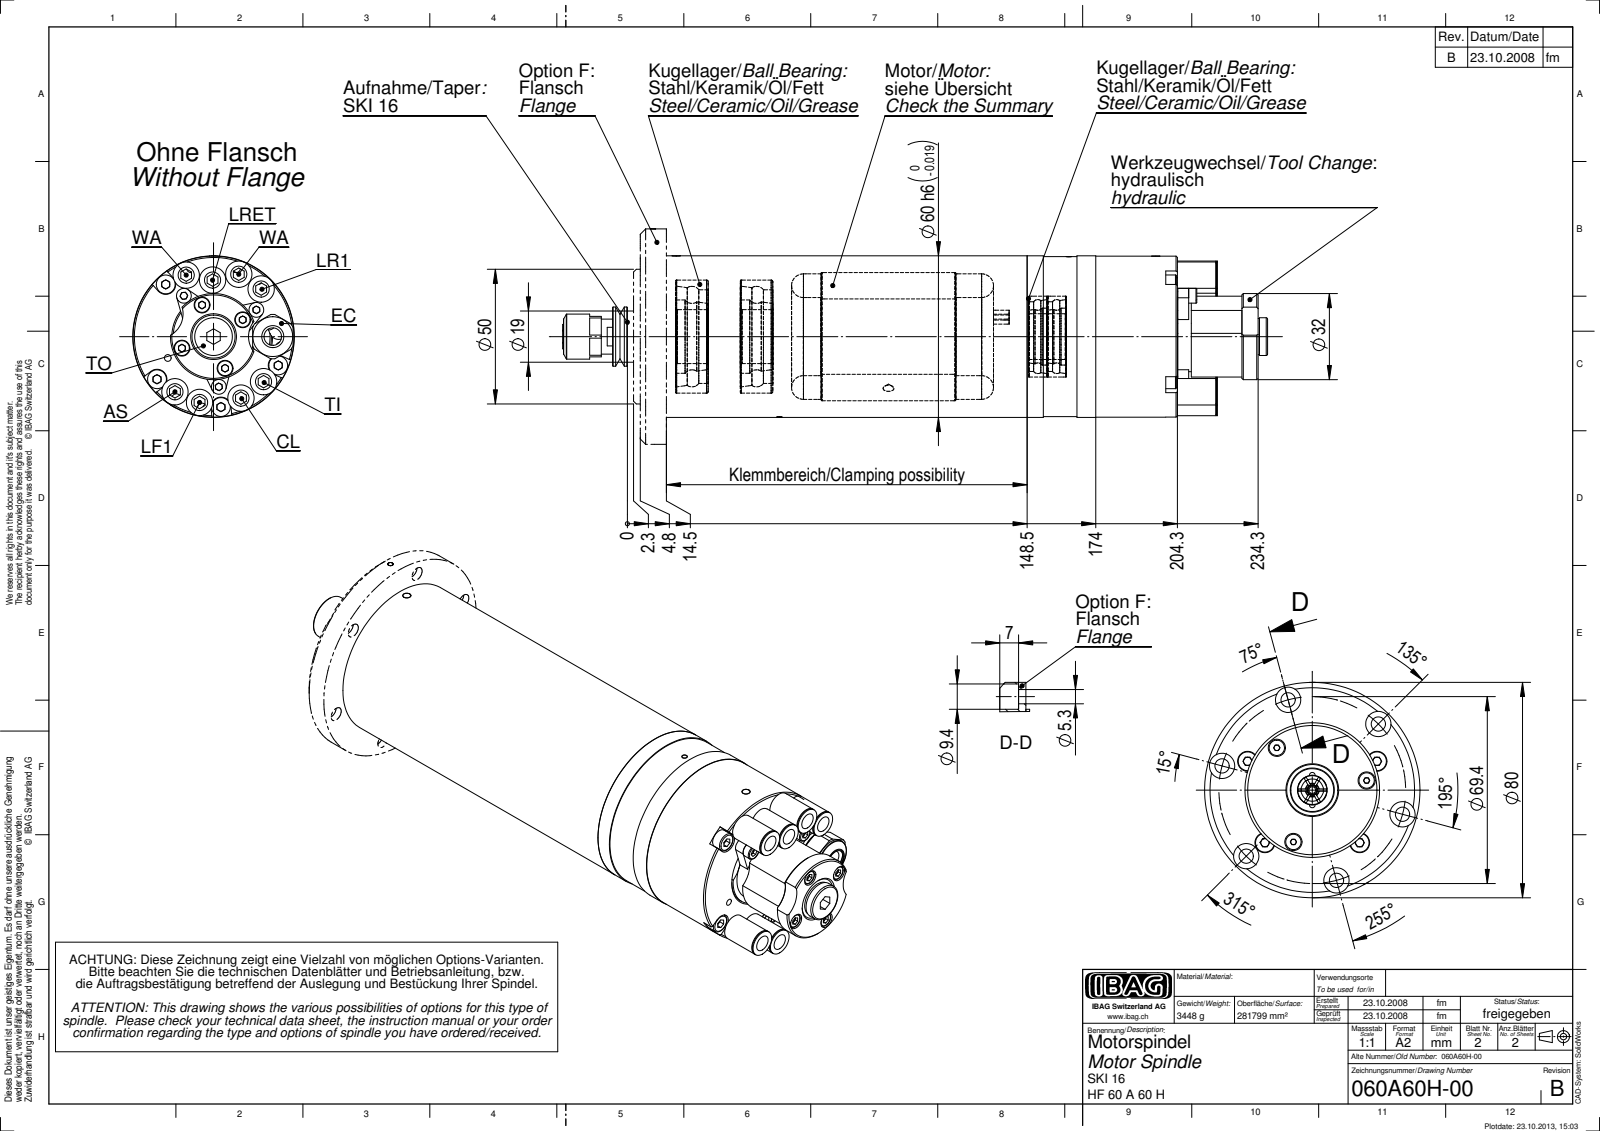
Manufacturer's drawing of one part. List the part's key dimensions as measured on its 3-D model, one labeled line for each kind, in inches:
Part name (STEP PRODUCT): 060A60H-00B
STEP written by: SolidWorks 2009 (CONFIG_CONTROL_DESIGN)
Units: inches
Bodies: 0 solids, 536 faces (254 planar, 178 cylindrical, 104 other)
Overall size (bounding box): 10.309 × 2.362 × 2.362
Round holes (diameter × count): ⌀0.236 ×8, ⌀0.232 ×4, ⌀0.079 ×2, ⌀0.118 ×2, ⌀0.165 ×1, ⌀0.256 ×1, ⌀0.323 ×1
Round bosses / shafts (diameter × count): ⌀0.386 ×8, ⌀0.276 ×8, ⌀0.224 ×3, ⌀0.217 ×3, ⌀2.362 ×1, ⌀2.354 ×1, ⌀1.969 ×1, ⌀1.181 ×1
Partial cylindrical surfaces — rounded edges, fillets, slot ends (radius × count): R0.146 ×8, R0.354 ×2, R0.325 ×1, R0.63 ×1
Main face-to-face distances: 0.382, 7.854, 7.472, 0.098, 0.48, 7.953, 5.756, 5.657, 5.276, 2.197
Hole centre spacings: 0.984, 0.493, 0.393, 0.494, 0.696, 1.446, 1.476, 1.961
